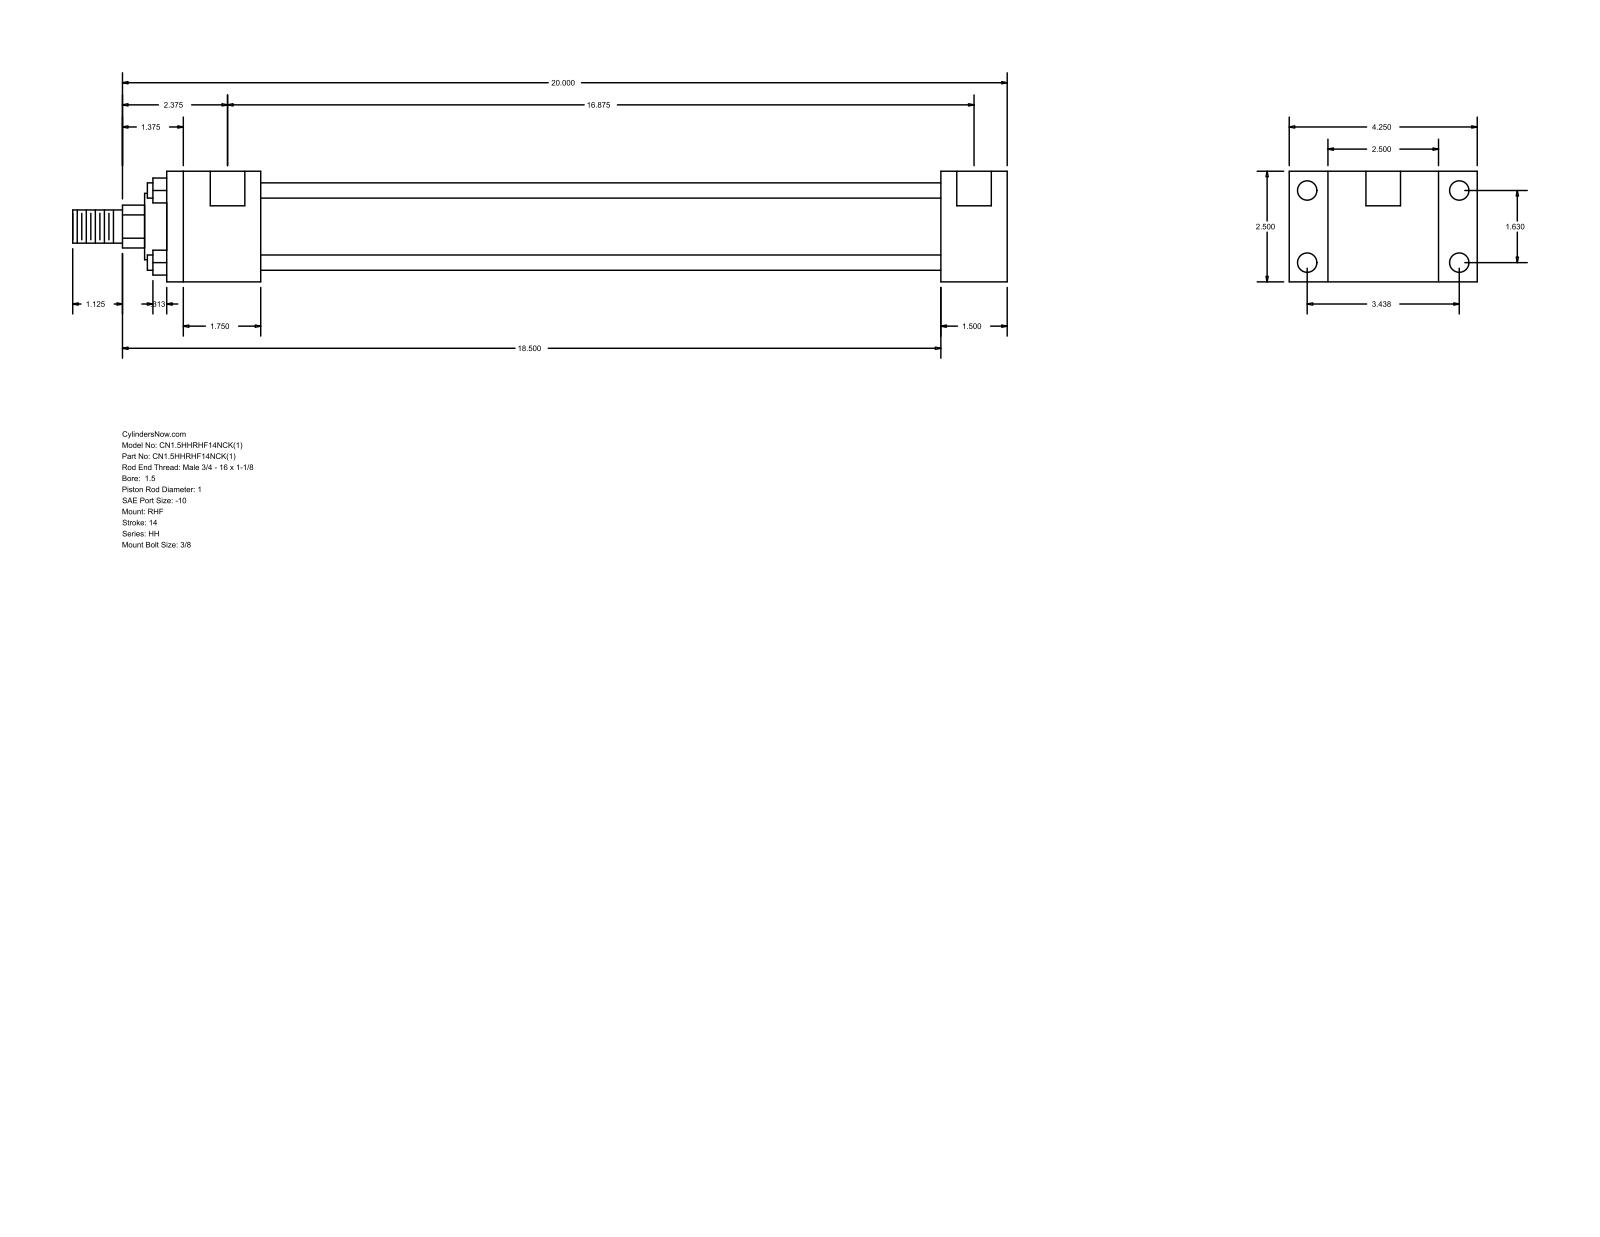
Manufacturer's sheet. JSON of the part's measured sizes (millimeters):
{"part_name": "HH_RHF__0150_1", "step_written_by": "GSSL Pune (CONFIG_CONTROL_DESIGN)", "units": "millimeters", "bodies": {"solids": 0, "faces": 88, "planar": 60, "cylindrical": 28, "other": 0}, "overall_size": [536.58, 107.95, 63.5], "round_holes": [[5.56, 4], [11.13, 4], [19.84, 2]], "round_bosses_or_shafts": [[8.76, 4], [44.45, 1], [38.1, 1], [25.4, 1], [19.05, 1]], "partial_cylinders_radius": [[12.29, 1]], "face_to_face_distances": [63.5, 22.23, 85.73, 38.1, 107.96, 390.52, 428.62, 53.98, 444.5, 482.6], "hole_center_spacings": [1.59, 41.4, 87.32, 96.64, 430.21, 431.8, 428.62]}
